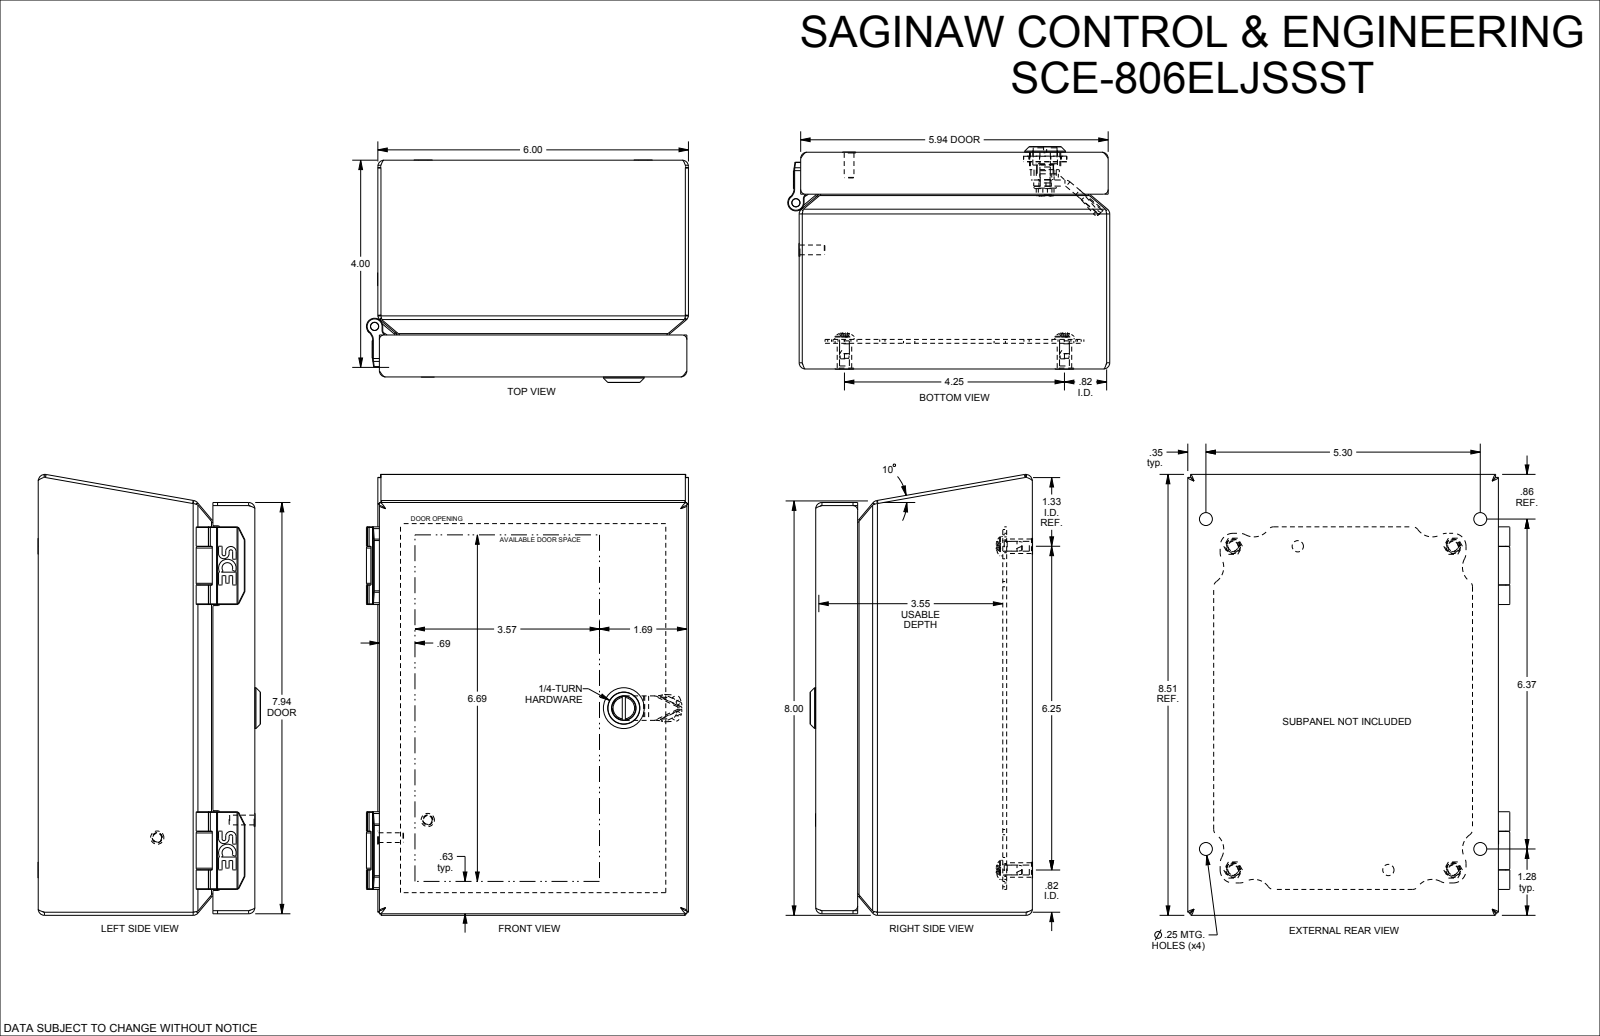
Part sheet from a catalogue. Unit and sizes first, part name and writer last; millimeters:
Units: millimetres
Overall size (bounding box): 216 × 158 × 109.1
Round holes (diameter × count): ⌀4.1 ×4, ⌀4.8 ×4, ⌀6.4 ×4, ⌀7.2 ×4, ⌀0.5 ×2, ⌀2.5 ×2, ⌀5.5 ×2, ⌀6.8 ×2, ⌀4 ×1, ⌀5 ×1, ⌀5.1 ×1, ⌀6.1 ×1
Round bosses / shafts (diameter × count): ⌀4.8 ×6, ⌀12.3 ×4, ⌀9.5 ×4, ⌀7.1 ×4, ⌀6 ×4, ⌀4.1 ×4, ⌀6.6 ×2, ⌀6.5 ×2
Partial cylindrical surfaces — rounded edges, fillets, slot ends (radius × count): R0.8 ×50, R0.2 ×24, R0.3 ×21, R6.4 ×13, R3.2 ×11, R0.3 ×10, R1.5 ×10, R8.7 ×8
Main face-to-face distances: 1.5, 1.5, 150.9, 106.3, 104.8, 104.8, 103.3, 14.5, 13, 90.3
Hole centre spacings: 139.7, 0.5, 16.8, 18.9, 31.8, 76.2, 79.9, 108
Volume: 309 900 mm³ · Surface area: 379 600 mm²
Bodies: 34 solids, 1454 faces (566 planar, 353 cylindrical, 535 other)
Part name (STEP PRODUCT): SCE-806ELJSSST
STEP written by: SolidWorks 2021 (AUTOMOTIVE_DESIGN)
